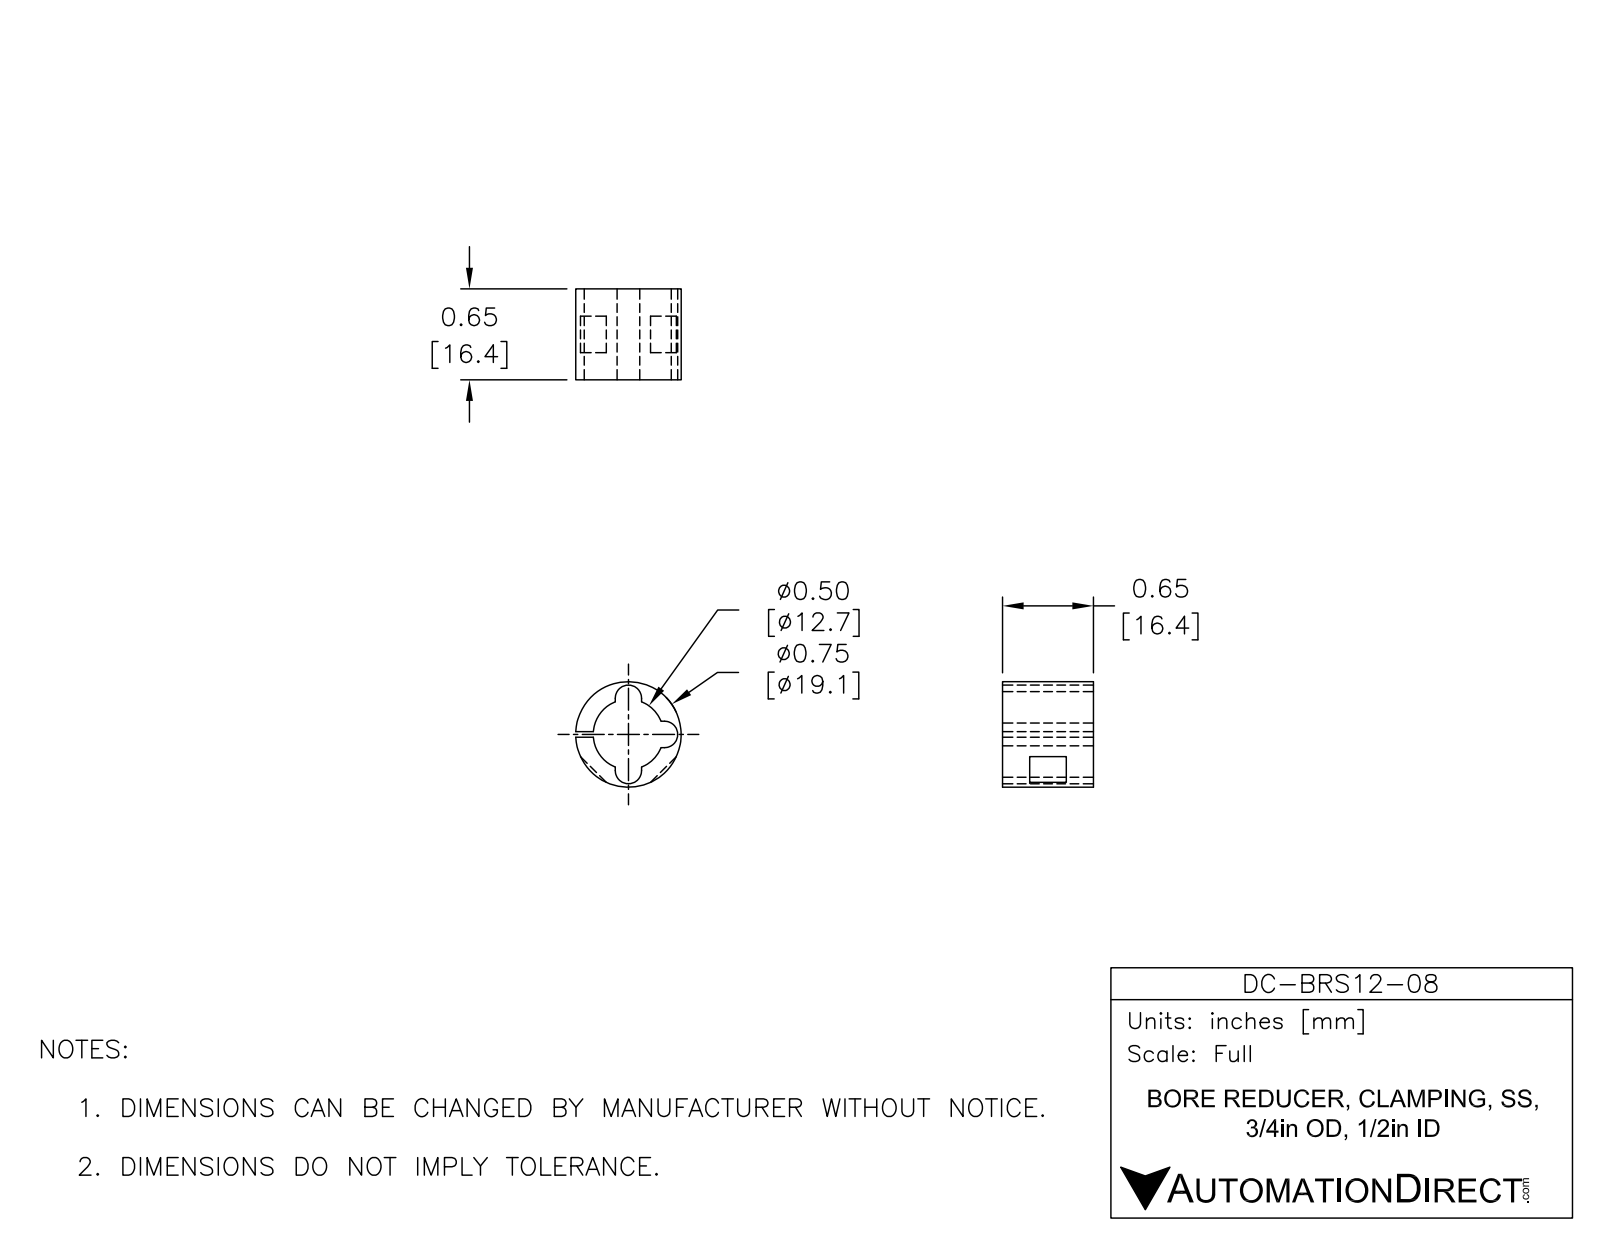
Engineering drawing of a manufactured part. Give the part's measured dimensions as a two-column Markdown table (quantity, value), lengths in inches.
| quantity | value |
| --- | --- |
| part name | DC-BRS12-08 |
| STEP written by | SolidWorks 2015 (AUTOMOTIVE_DESIGN) |
| units | inches |
| bodies | 1 solid, 27 faces (16 planar, 11 cylindrical, 0 other) |
| overall size | 0.75 × 0.75 × 0.646 |
| volume | 0.122 in³ |
| surface area | 3.339 in² |
| round bosses / shafts (diameter × count) | 0.75 × 1 |
| partial cylindrical surfaces (radius × count) | 0.094 × 3, 0.25 × 1 |
| main face-to-face distances | 0.646, 0.04, 0.187, 0.074, 0.114, 0.193, 0.453, 0.26 |
